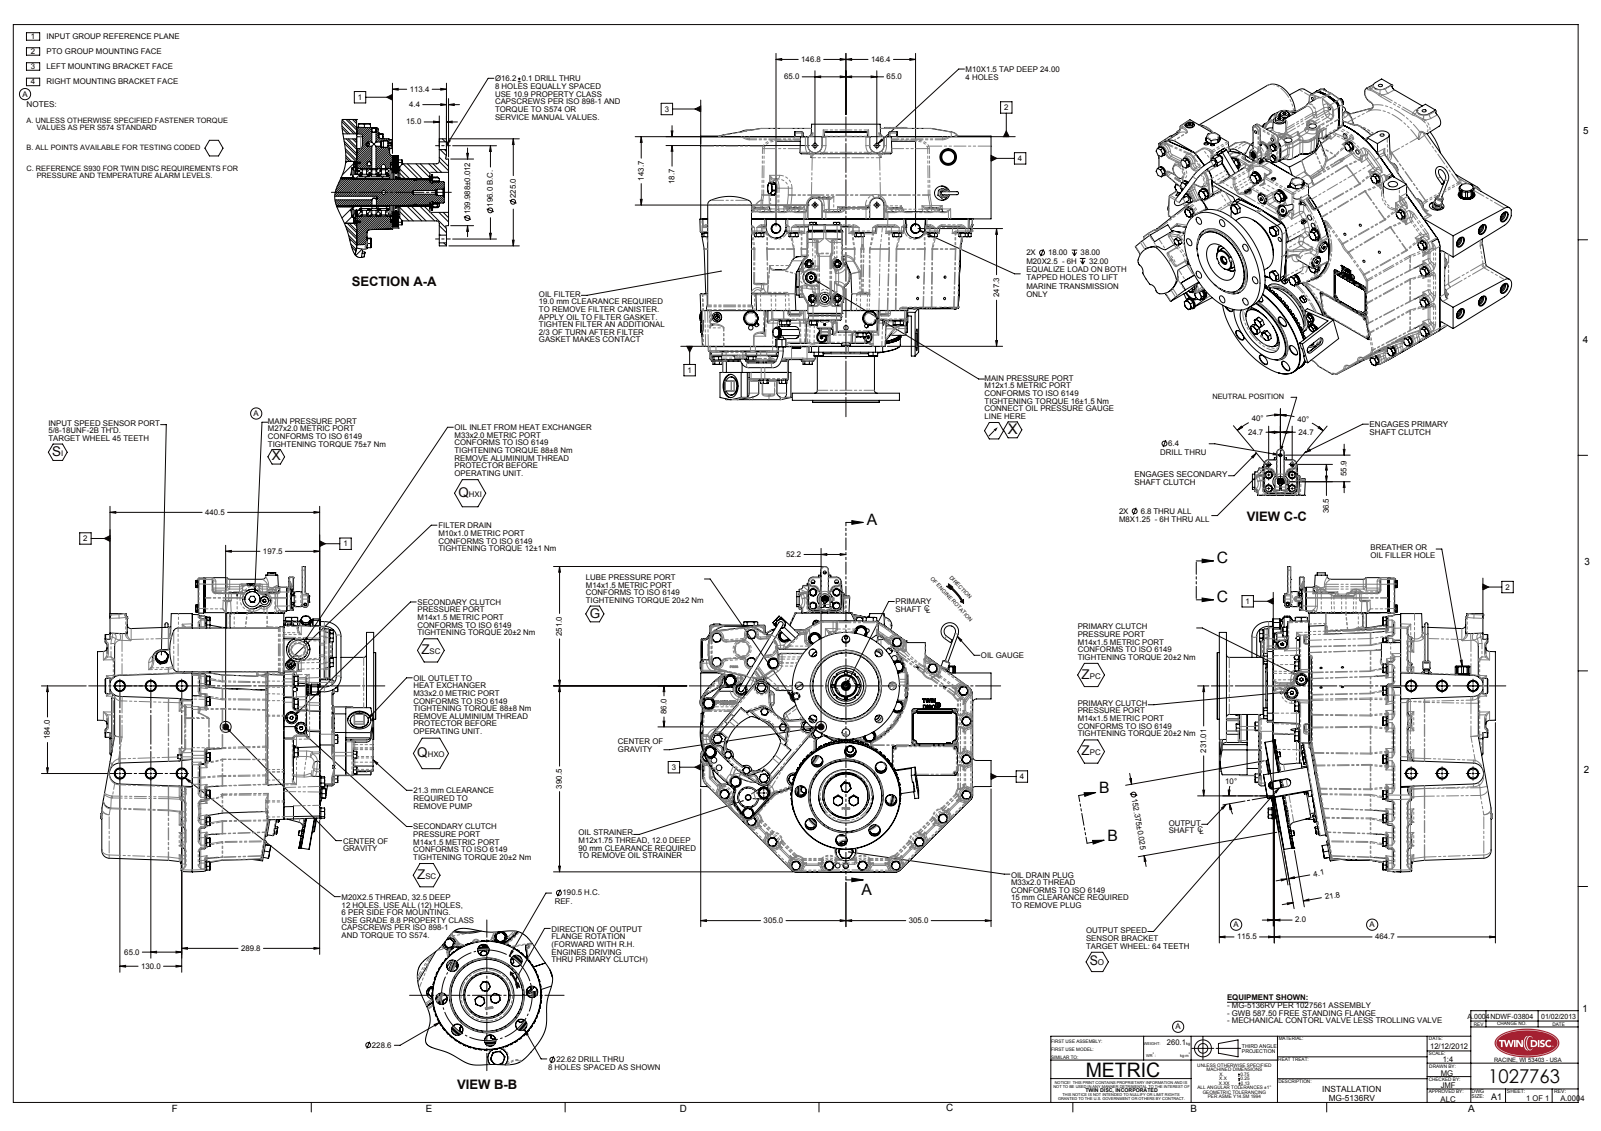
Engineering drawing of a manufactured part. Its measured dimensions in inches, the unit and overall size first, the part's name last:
Units: inches
Overall size (bounding box): 25.262 × 24.091 × 23.015
Round holes (diameter × count): ⌀0.346 ×21, ⌀0.421 ×9, ⌀0.906 ×9, ⌀0.984 ×9, ⌀0.638 ×8, ⌀0.891 ×8, ⌀0.817 ×6, ⌀0.394 ×5, ⌀0.197 ×4, ⌀0.268 ×4, ⌀0.315 ×4, ⌀0.65 ×4
Round bosses / shafts (diameter × count): ⌀0.781 ×26, ⌀0.945 ×14, ⌀0.748 ×8, ⌀0.394 ×6, ⌀0.512 ×5, ⌀0.551 ×4, ⌀0.669 ×3, ⌀0.492 ×3
Partial cylindrical surfaces — rounded edges, fillets, slot ends (radius × count): R0.118 ×144, R0.315 ×74, R1.563 ×69, R0.256 ×60, R0.098 ×52, R0.236 ×36, R0.079 ×35, R0.06 ×28
Main face-to-face distances: 0.015, 0.017, 7.589, 7.574, 7.572, 7.557, 10.542, 2.953, 2.968, 10.525
Hole centre spacings: 5.303, 6.929, 2.87, 7.5, 2.87, 2.756, 6.929, 2.87
Bodies: 0 solids, 5783 faces (1739 planar, 1524 cylindrical, 2520 other)
Part name (STEP PRODUCT): 1027763
STEP written by: SolidWorks 2010 (AUTOMOTIVE_DESIGN)
